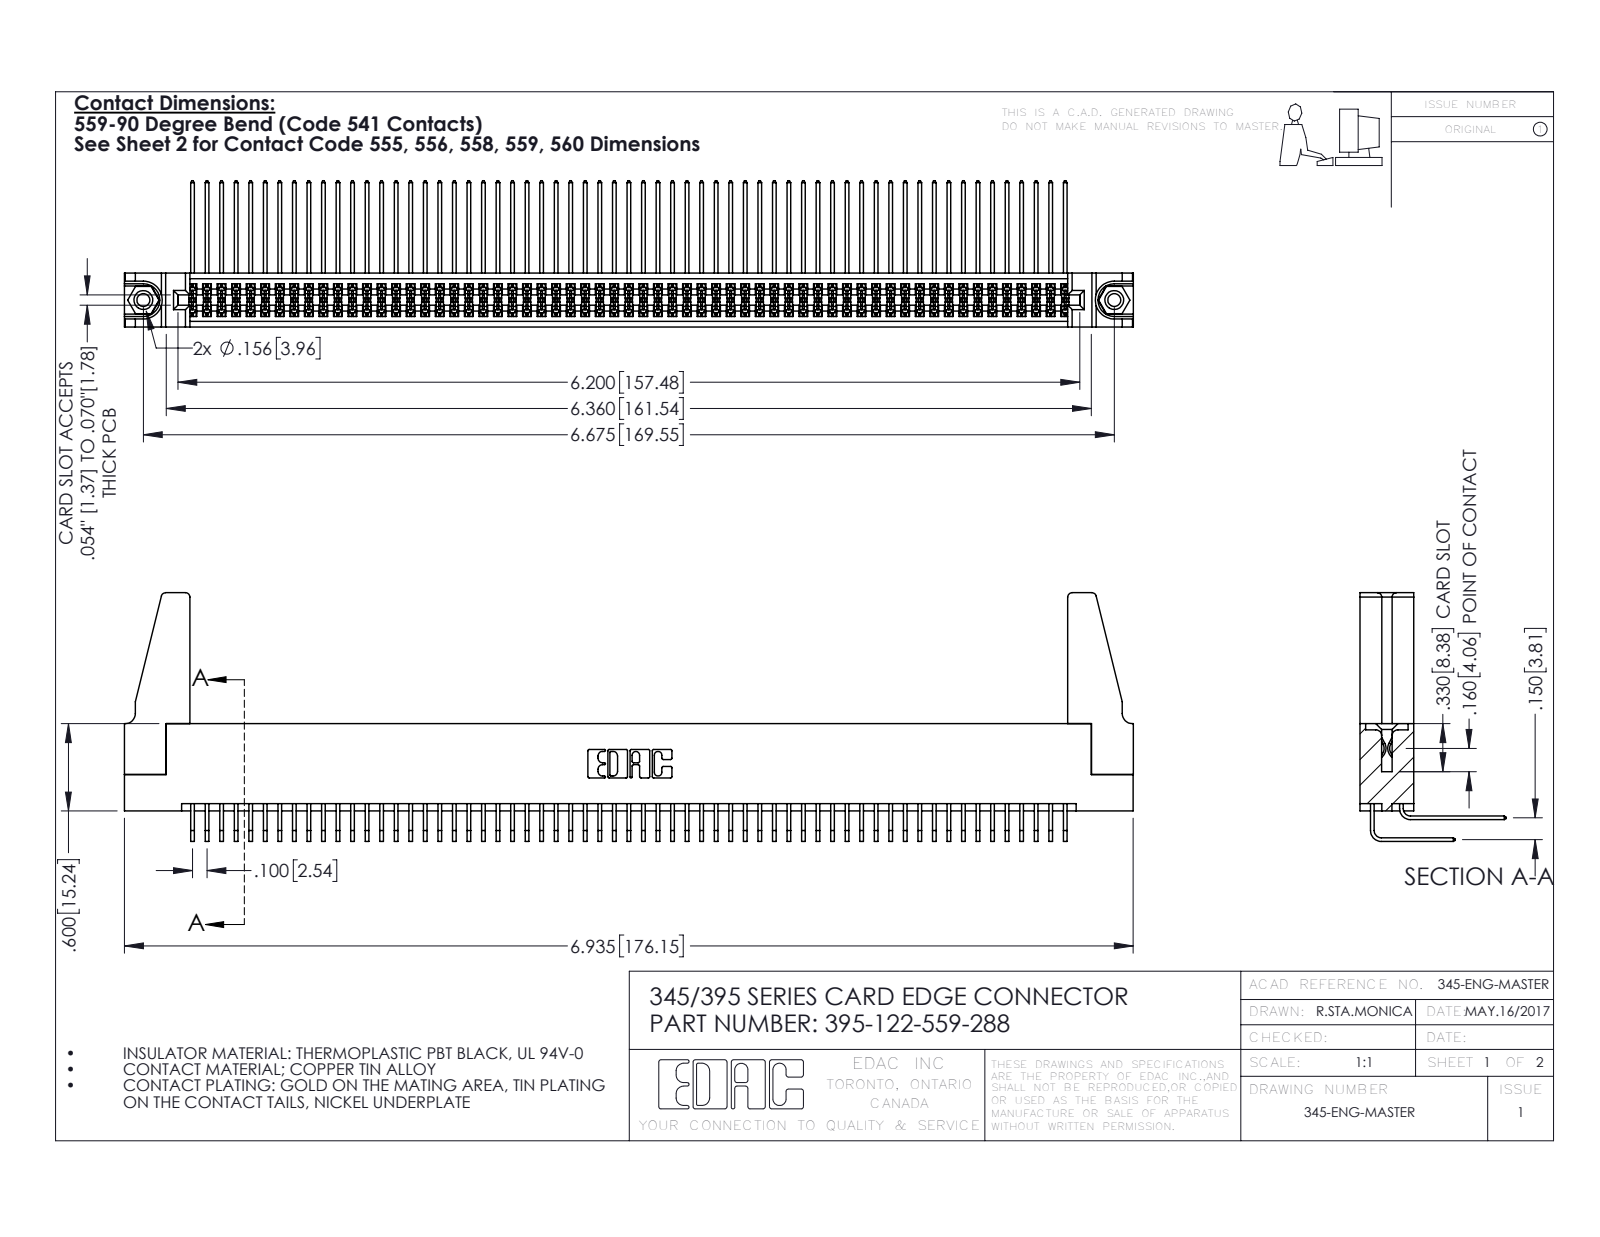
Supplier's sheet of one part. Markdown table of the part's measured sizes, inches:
| quantity | value |
| --- | --- |
| part name | 395-122-559-288; 345-250-001_345-250-001-102; 345-292-001_558 559 Tail - 1; 345-292-001_559 Tail - 2 (+2 more) |
| STEP written by | SolidWorks 2016 (CONFIG_CONTROL_DESIGN) |
| units | inches |
| bodies | 127 solids, 6594 faces (4422 planar, 2156 cylindrical, 16 other) |
| overall size | 6.936 × 1.709 × 1.005 |
| volume | 1.297 in³ |
| surface area | 51.77 in² |
| round holes (diameter × count) | 0.089 × 2, 0.125 × 2, 0.156 × 2, 0.064 × 1 |
| round bosses / shafts (diameter × count) | 0.155 × 2 |
| partial cylindrical surfaces (radius × count) | 0.006 × 183, 0.01 × 22, 0.03 × 8, 0.007 × 6, 0.031 × 6, 0.026 × 3, 0.014 × 2, 0.019 × 2 |
| main face-to-face distances | 0.072, 0.298, 0.37, 0.2, 0.098, 0.272, 0.025, 0.225, 0.175, 0.15 |
| hole center spacings | 0.27, 6.439, 6.675 |
